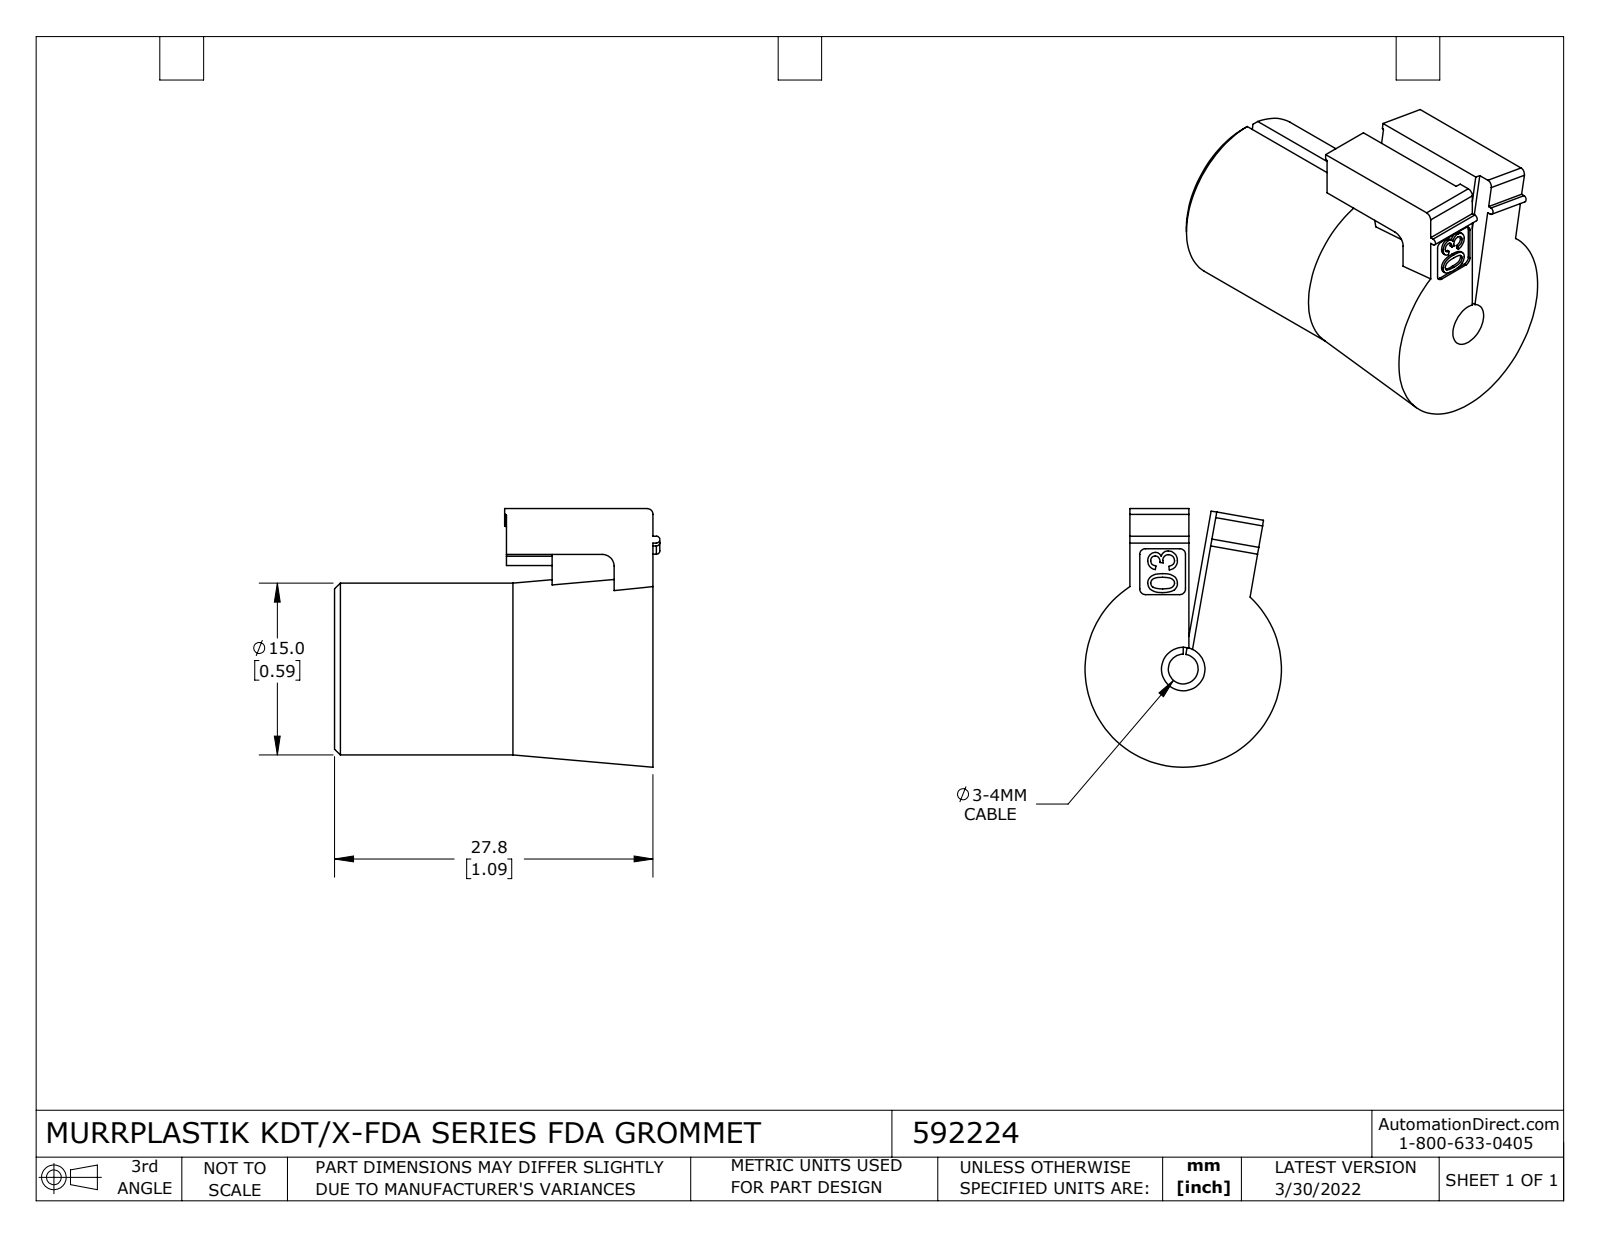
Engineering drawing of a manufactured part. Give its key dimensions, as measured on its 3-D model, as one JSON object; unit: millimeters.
{"part_name": "592224", "step_written_by": "SolidWorks 2021 (CONFIG_CONTROL_DESIGN)", "units": "millimeters", "bodies": {"solids": 1, "faces": 111, "planar": 49, "cylindrical": 24, "other": 38}, "overall_size": [28.4, 22.6, 17.1], "volume_mm3": 5390, "surface_area_mm2": 2867, "round_holes": [[2.6, 1], [3.8, 1]], "round_bosses_or_shafts": [[15, 1]], "partial_cylinders_radius": [[0.5, 6], [0.1, 2], [0.3, 2], [1, 2]], "face_to_face_distances": [27.8, 4.6, 4, 0.5, 12.8, 15, 4.1, 5.2, 8.8, 19]}
